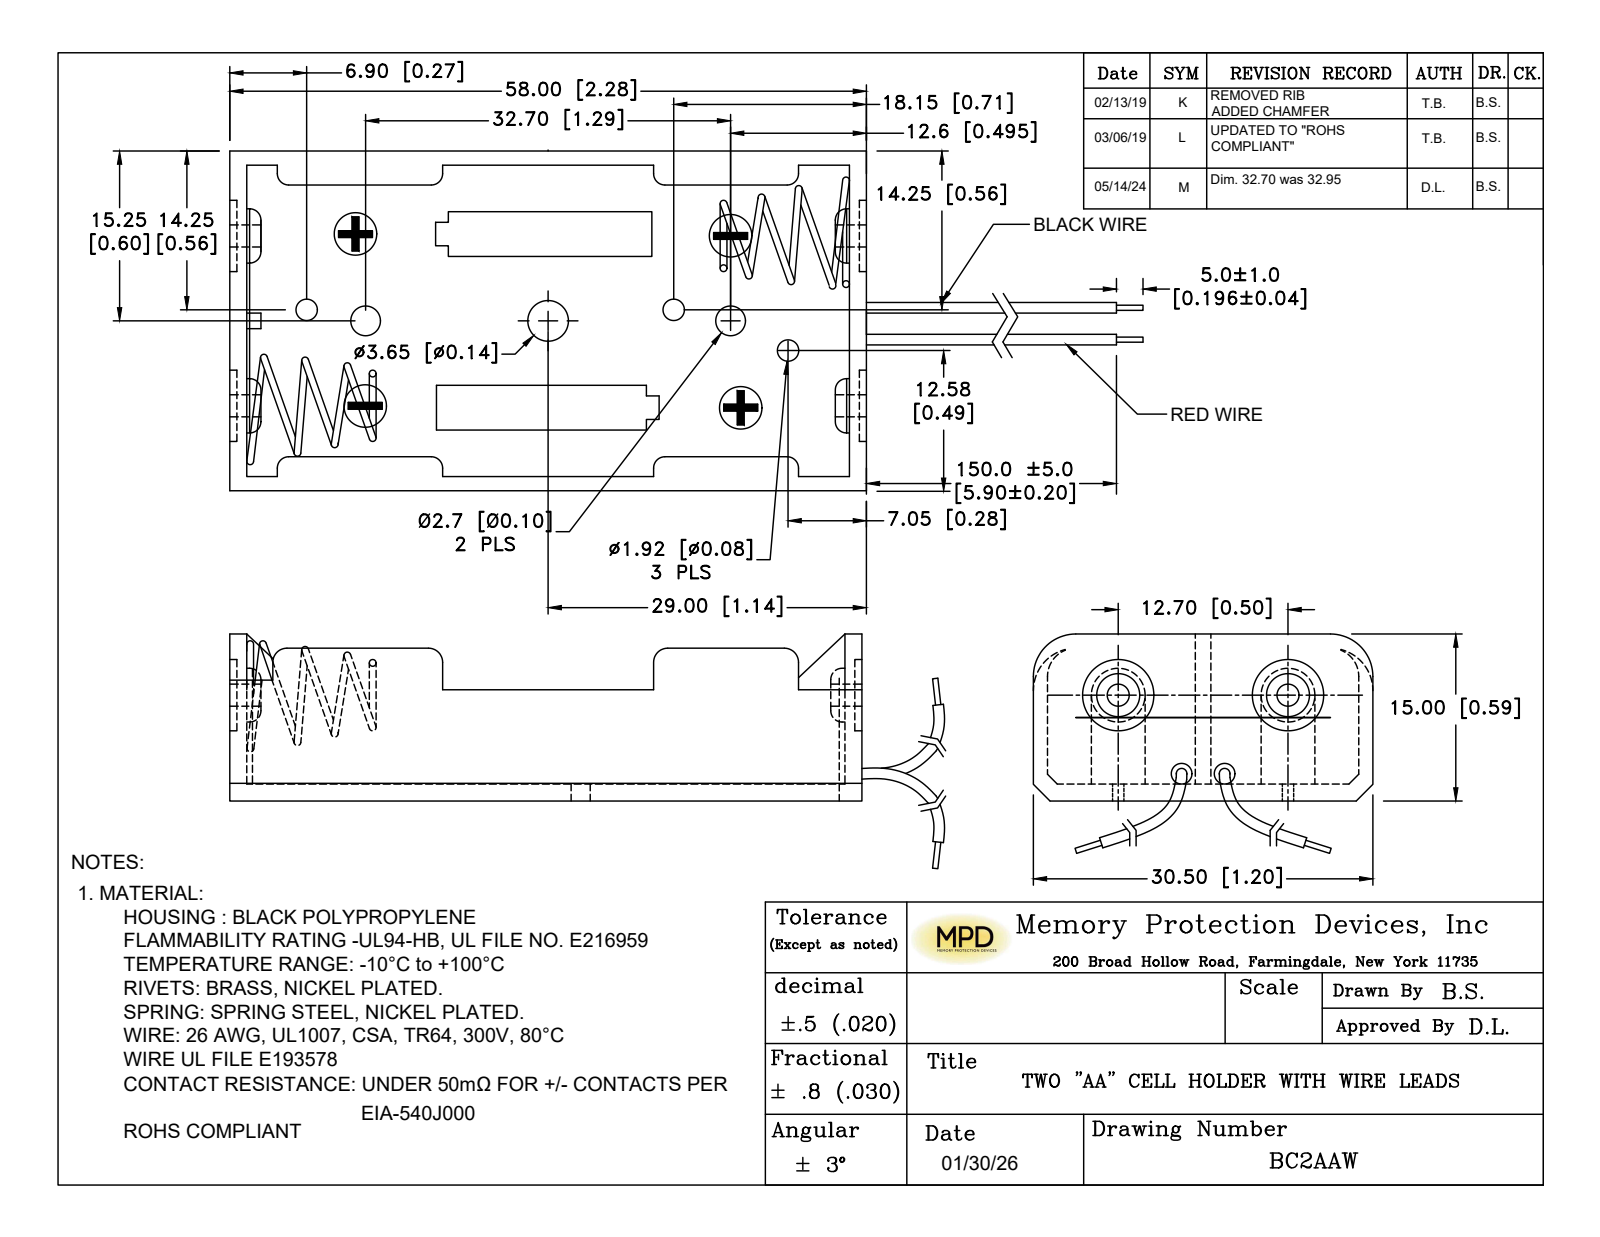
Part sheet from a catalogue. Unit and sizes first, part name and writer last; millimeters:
Units: millimetres
Overall size (bounding box): 213 × 30.5 × 15
Round holes (diameter × count): ⌀3.7 ×4, ⌀1.92 ×3, ⌀0.4 ×2, ⌀1.5 ×2, ⌀2 ×2, ⌀2.3 ×2, ⌀2.7 ×2, ⌀3 ×2, ⌀7.6 ×2, ⌀3.65 ×1
Round bosses / shafts (diameter × count): ⌀4.7 ×4, ⌀6.2 ×2, ⌀3.5 ×2, ⌀0.81 ×2, ⌀0.6 ×2, ⌀0.7 ×1
Partial cylindrical surfaces — rounded edges, fillets, slot ends (radius × count): R2.5 ×8, R2.72 ×2, R2.95 ×2, R4 ×2
Main face-to-face distances: 1.1, 1.55, 29.4, 56.9, 30.5, 55.8, 28.3, 58, 0.31, 57.69
Hole centre spacings: 20.47, 5.64, 7.86, 10.06, 15.25, 32.95, 36.21, 36.36
Volume: 4 955 mm³ · Surface area: 10 100 mm²
Bodies: 10 solids, 356 faces (170 planar, 132 cylindrical, 54 other)
Part name (STEP PRODUCT): BC2AAW
STEP written by: SolidWorks 2017 (AUTOMOTIVE_DESIGN)
